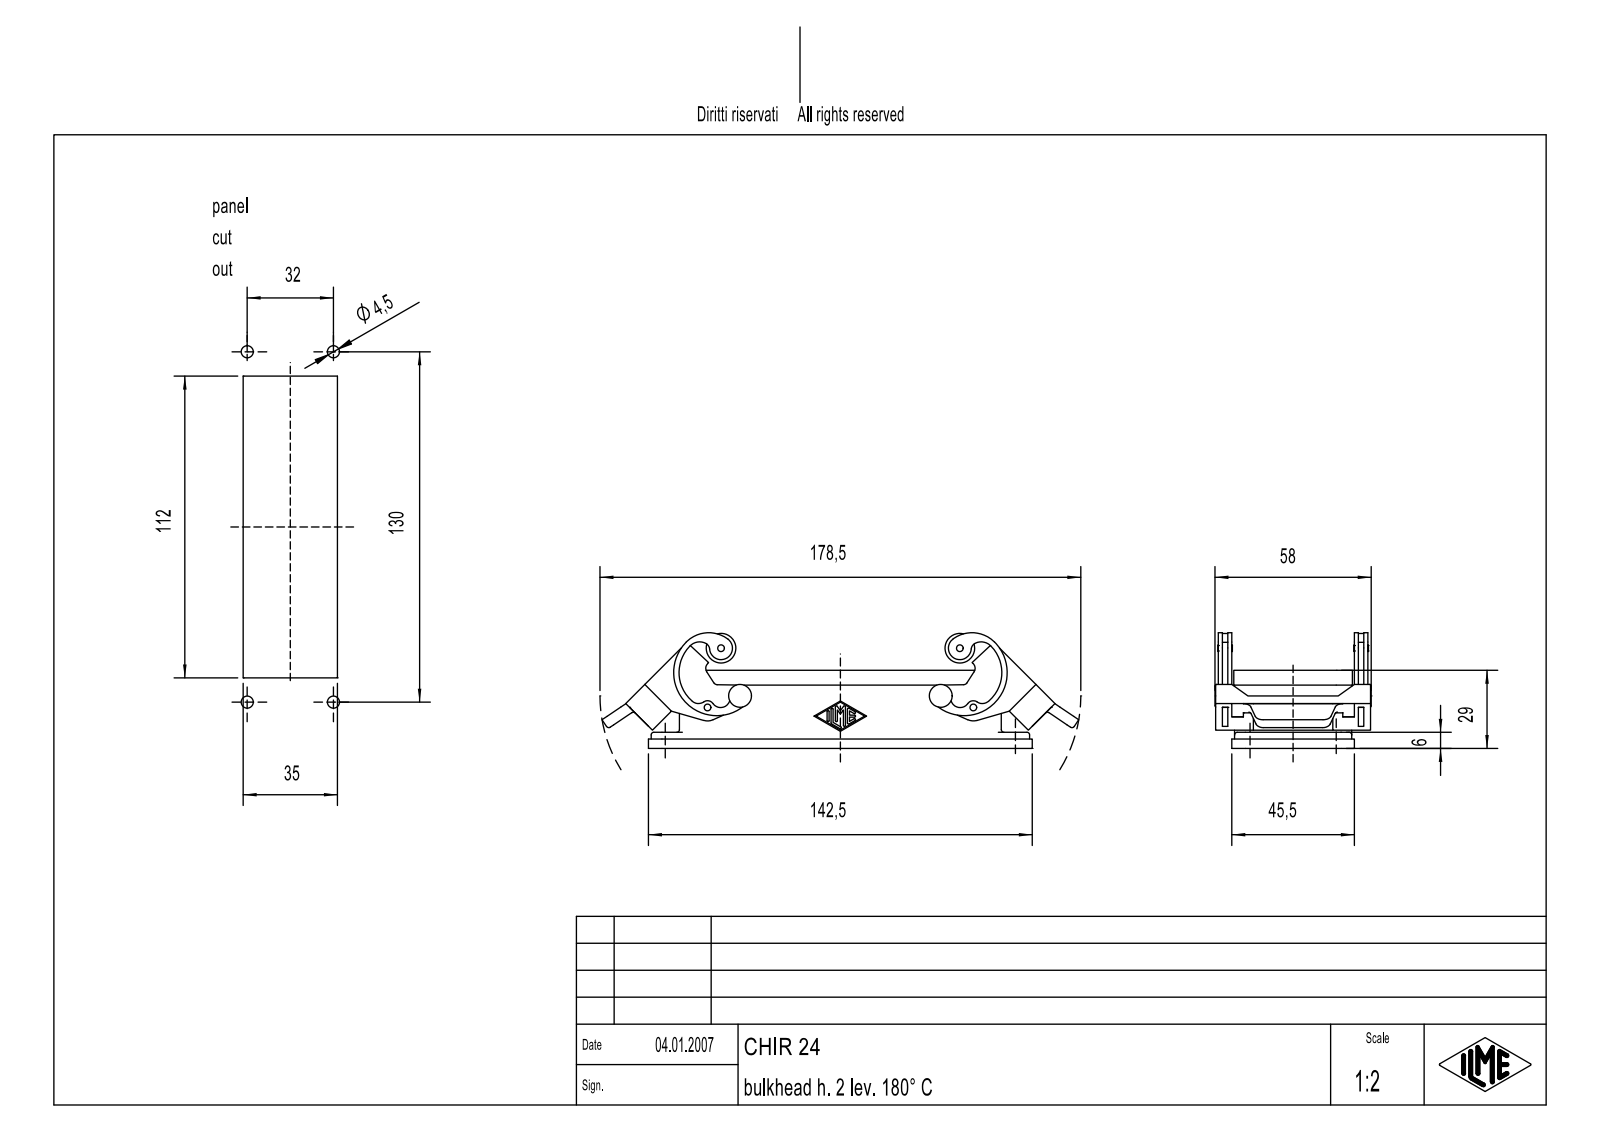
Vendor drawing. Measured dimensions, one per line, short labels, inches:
name: MSBO12385
written by: Creo Elements/Direct Modeling 17.0D 15-Jul-2011 (C) Parametric Technology GmbH (AUTOMOTIVE_DESIGN)
unit: in
bodies: 1 solid, 609 faces (251 planar, 278 cylindrical, 80 other)
size: 6.968 × 2.283 × 1.691
volume: 3.567 in³; area: 62.73 in²
holes: 4× ⌀0.097, 4× ⌀0.122, 4× ⌀0.177, 4× ⌀0.181, 2× ⌀0.079, 2× ⌀0.098
bosses: 2× ⌀0.433, 2× ⌀0.197, 2× ⌀0.118
rounds: 16× R0.039, 14× R0.015, 12× R0.118, 10× R0.098, 8× R0.138, 8× R0.197, 8× R0.236, 6× R0.059
face distances: 0.118, 0.157, 1.594, 0.039, 1.988, 0.138, 0.098, 0.03, 0.059, 0.177
hole spacings: 0.521, 1.269, 4.607, 4.75, 1.063, 1.26, 4.094, 4.23
